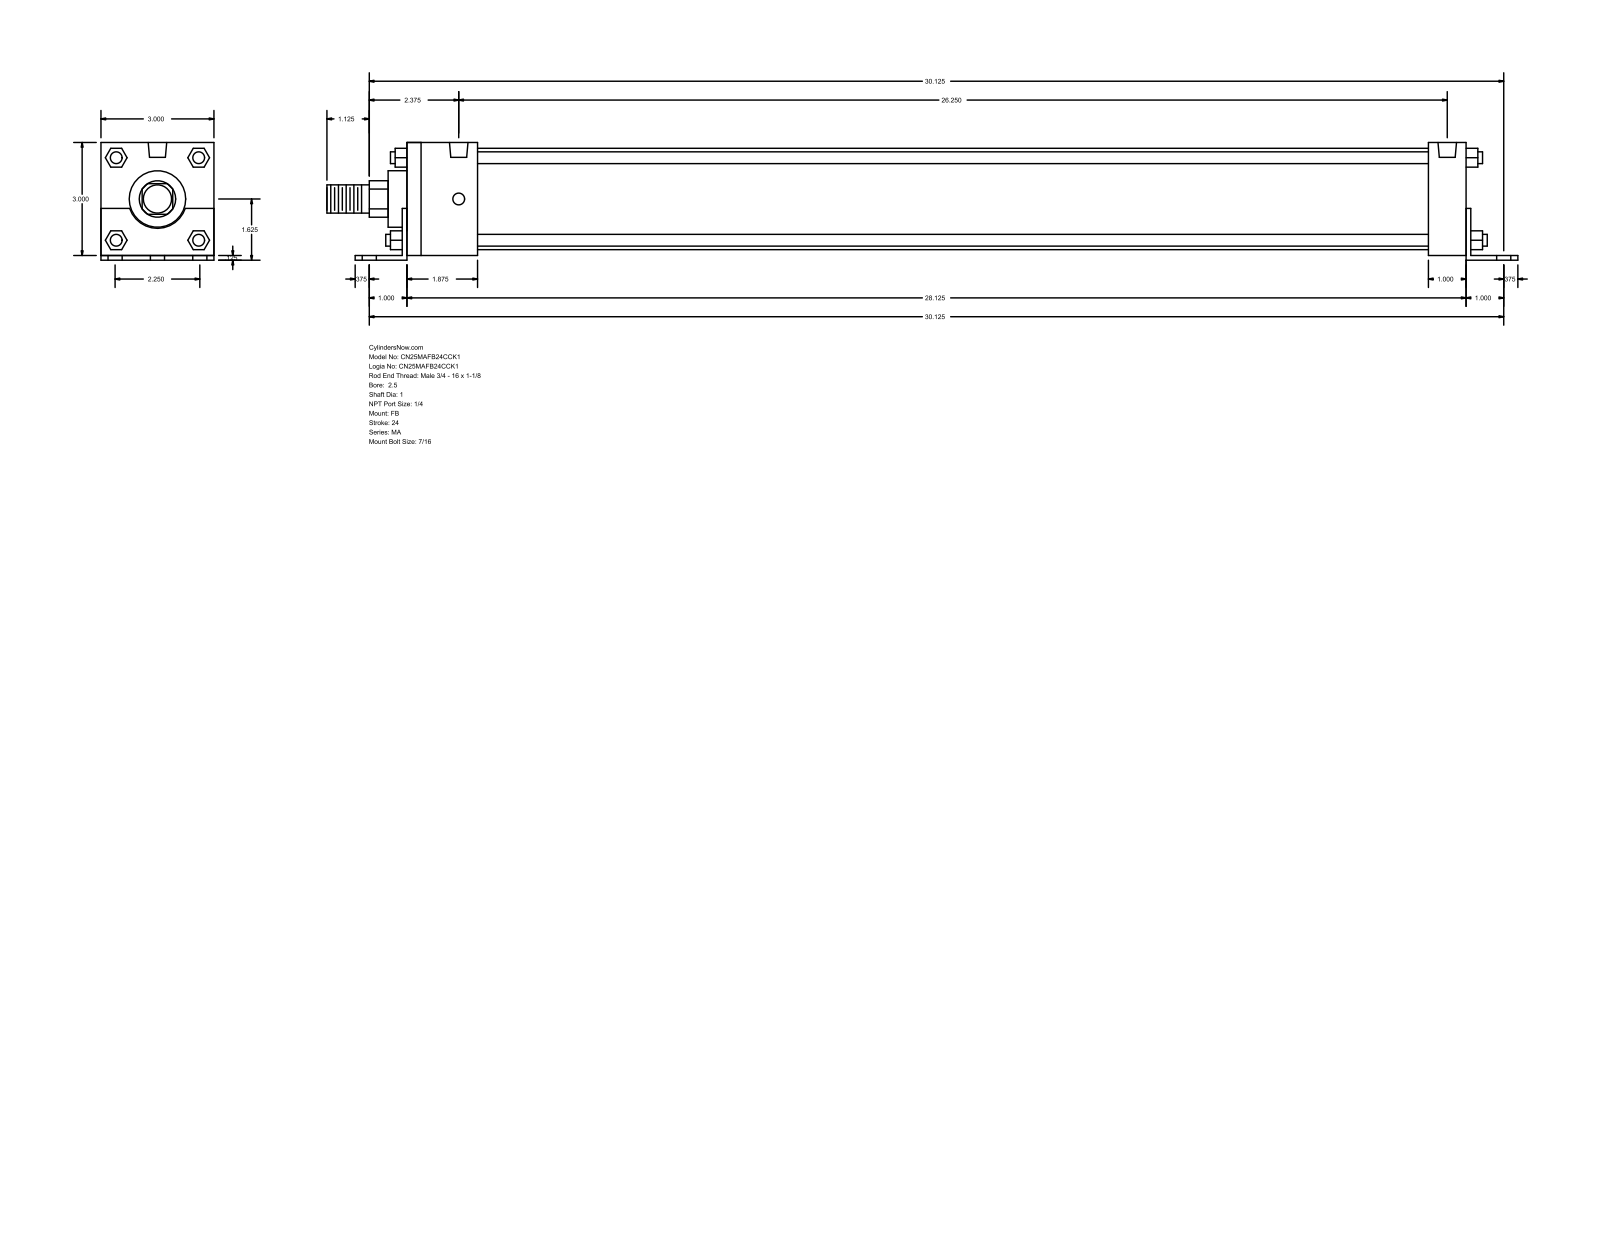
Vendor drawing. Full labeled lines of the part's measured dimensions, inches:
Part name (STEP PRODUCT): MA_FB__0250_1
STEP written by: GSSL Pune (CONFIG_CONTROL_DESIGN)
Units: inches
Bodies: 0 solids, 140 faces (105 planar, 35 cylindrical, 0 other)
Overall size (bounding box): 31.625 × 3.125 × 3
Round holes (diameter × count): ⌀0.437 ×6, ⌀0.313 ×4, ⌀0.492 ×2
Round bosses / shafts (diameter × count): ⌀0.313 ×4, ⌀2.69 ×1, ⌀1.5 ×1, ⌀1 ×1, ⌀0.75 ×1
Partial cylindrical surfaces — rounded edges, fillets, slot ends (radius × count): R0.484 ×1, R0.78 ×1
Main face-to-face distances: 3, 0.125, 3.125, 28.125, 0.125, 0.5, 28.25, 1.125, 2, 1.875
Hole centre spacings: 1.125, 30.146, 30.125, 1.874, 2.25, 2.628, 26.25, 27.772
